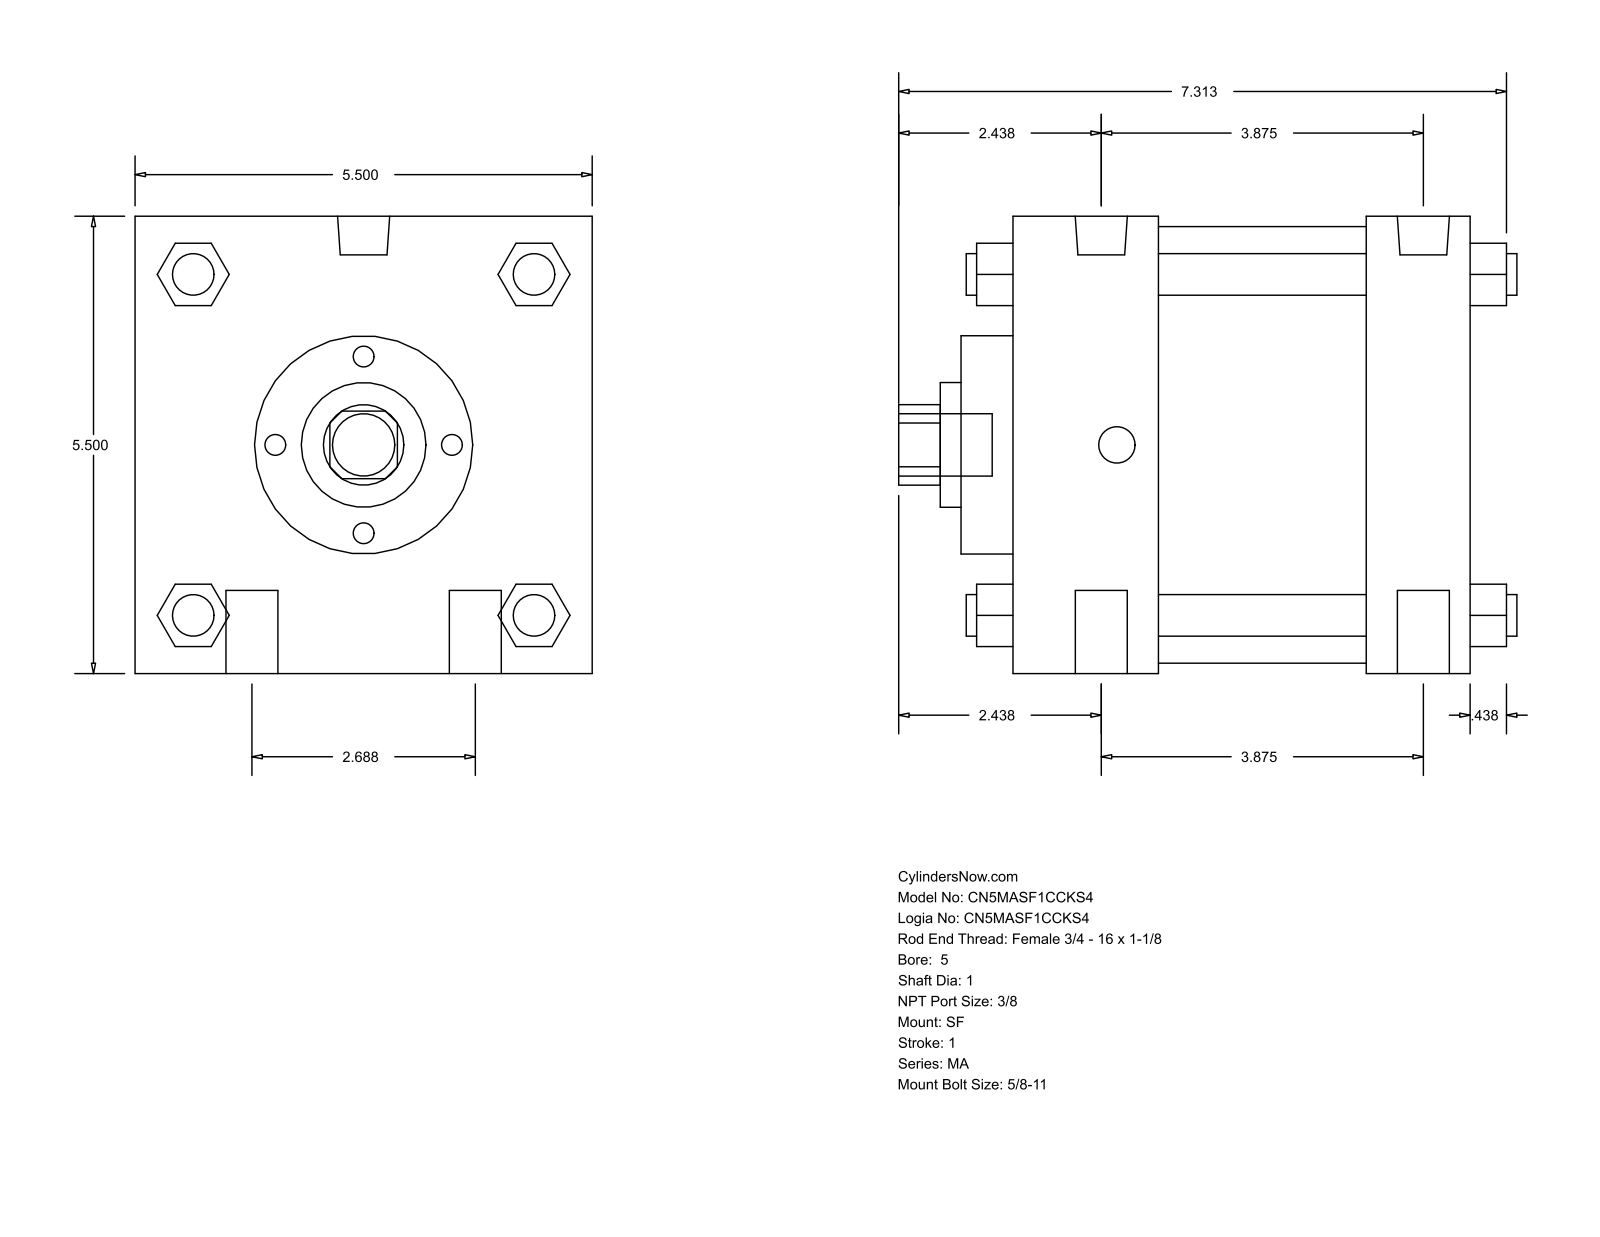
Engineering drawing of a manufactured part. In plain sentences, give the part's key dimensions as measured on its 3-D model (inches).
The part is named "MA_SF__0500_1". Its 3-D file was written by "GSSL Pune (CONFIG_CONTROL_DESIGN)". It is 0 solids with 126 faces: 95 planar, 31 cylindrical and 0 other. Overall it measures 7.437 by 5.5 by 5.5 inches. Round holes: 1 of diameter 1, 1 of diameter 1.5, 1 of diameter 2.625, 1 of diameter 5.25. Round bosses or shafts: 4 of diameter 0.625, 4 of diameter 0.5, 2 of diameter 0.627, 2 of diameter 0.437, 1 of diameter 0.75. Partial cylindrical surfaces (rounded edges, fillets, slot ends): 1 of radius 0.484. The main face-to-face distances are 5.5, 1.75, 4.25, 2.5, 3.75, 1.25, 0.625, 2.375, 4.875, 6.125.
